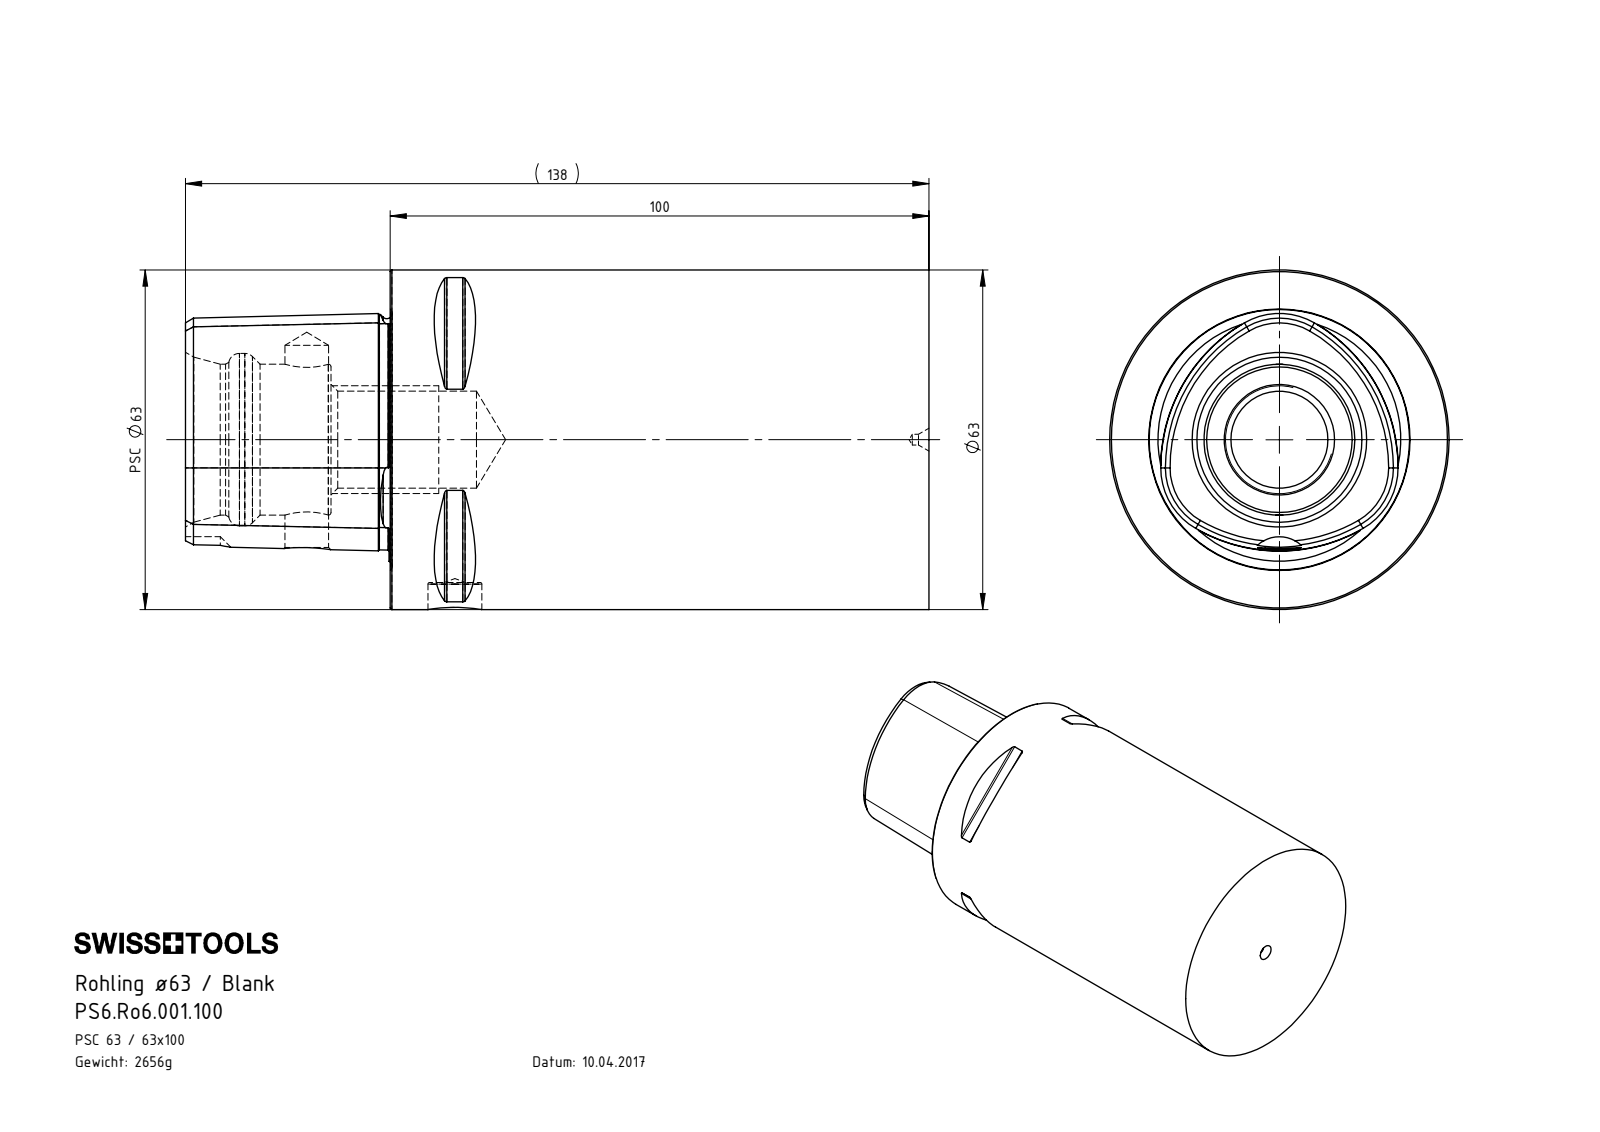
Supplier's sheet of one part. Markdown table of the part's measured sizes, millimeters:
| quantity | value |
| --- | --- |
| part name | PS6-Ro6.001.100_A |
| STEP written by | SolidWorks 2015 (CONFIG_CONTROL_DESIGN) |
| units | millimeters |
| bodies | 1 solid, 121 faces (19 planar, 27 cylindrical, 75 other) |
| overall size | 138 × 63 × 63 |
| volume | 338 723 mm³ |
| surface area | 35 479 mm² |
| round holes (diameter × count) | 2 × 1, 4 × 1, 8.1 × 1, 18 × 1, 28 × 1, 32 × 1 |
| round bosses / shafts (diameter × count) | 63 × 1 |
| partial cylindrical surfaces (radius × count) | 0.5 × 8, 6 × 1 |
| main face-to-face distances | 100, 38, 138, 24.88, 27, 11, 111, 55.8, 37.8, 10.8 |
| hole center spacings | 27.5 |
